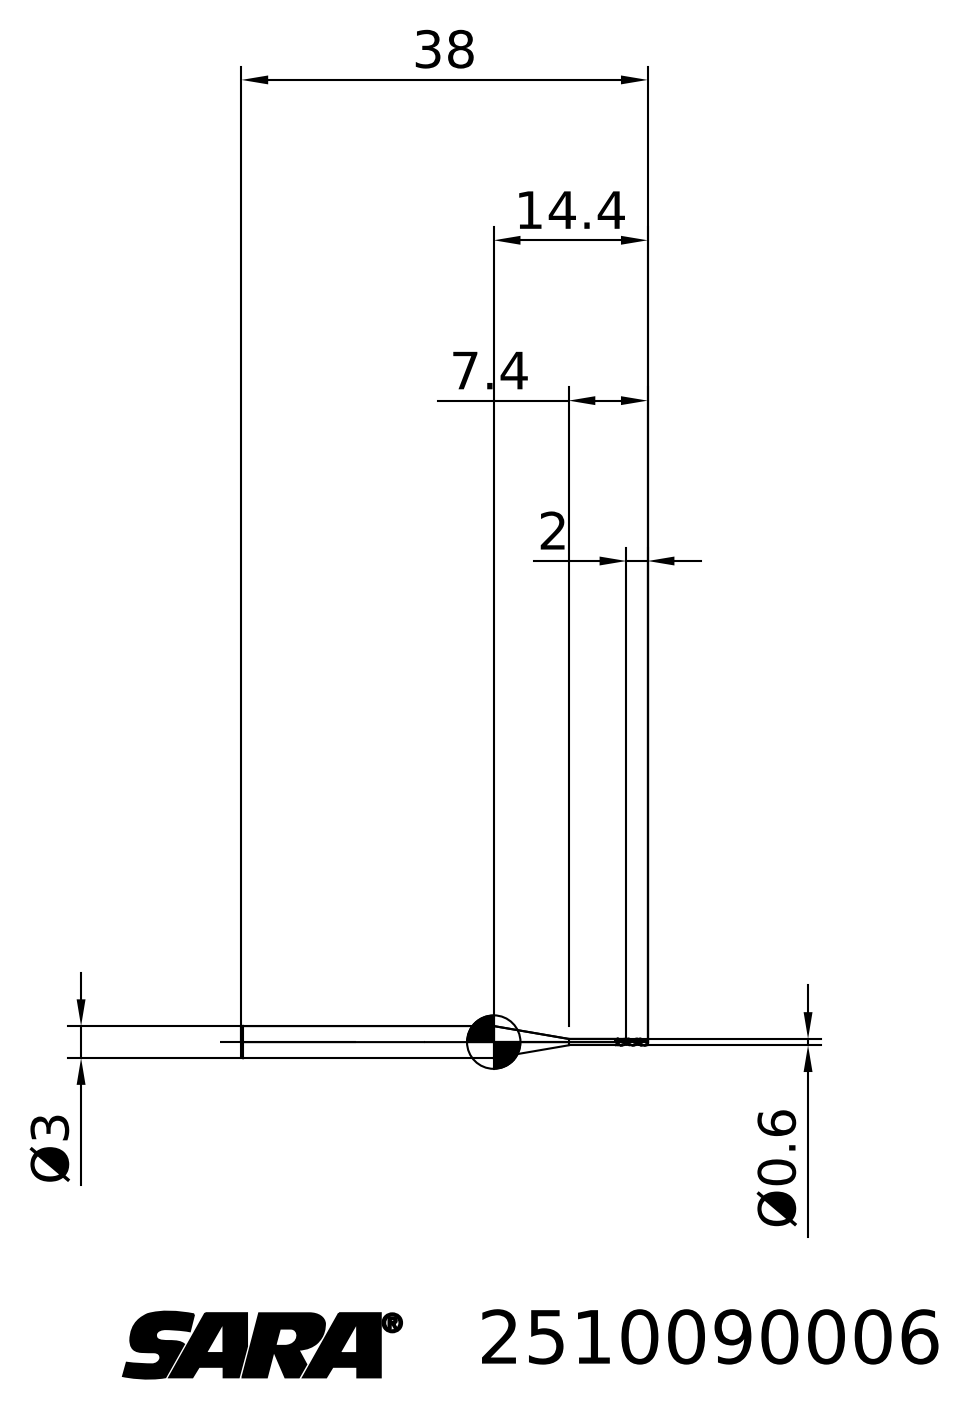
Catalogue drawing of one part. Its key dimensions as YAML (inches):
step_written_by: "TDM (AUTOMOTIVE_DESIGN)"
units: inches
bodies: {solids: 2, faces: 26, planar: 4, cylindrical: 0, other: 22}
overall_size: [1.496, 0.118, 0.118]
volume: 0.012
surface_area: 0.44
face_to_face_distances: [1.417, 0.079, 1.496]
